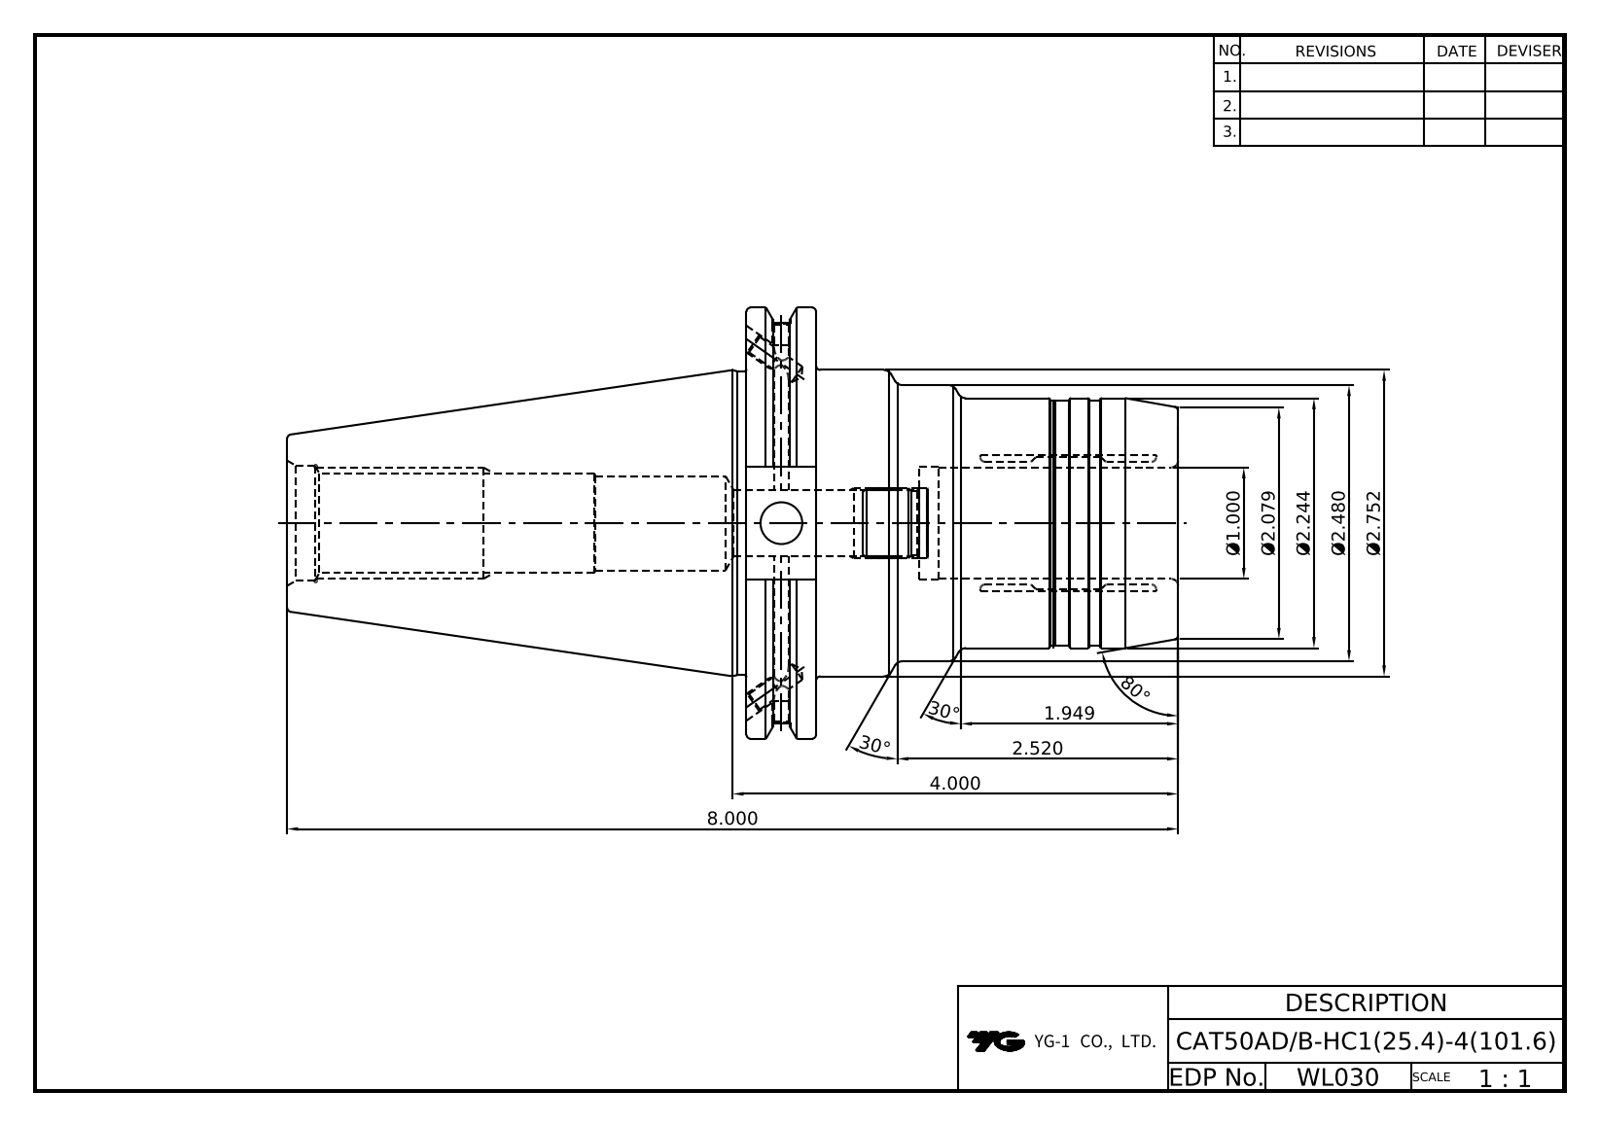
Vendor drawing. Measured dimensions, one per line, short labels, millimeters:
name: LO-CAT50ADB-HC25.4-101.6
written by: Autodesk Inventor 2022 (AUTOMOTIVE_DESIGN)
unit: mm
bodies: 1 solid, 110 faces (37 planar, 33 cylindrical, 40 other)
size: 203.2 × 98.42 × 94.69
volume: 527 991 mm³; area: 64 982 mm²
holes: 2× ⌀3.24, 2× ⌀4.13, 2× ⌀4.2, 2× ⌀5, 1× ⌀9.53, 1× ⌀14.92, 1× ⌀20.5, 1× ⌀21.97, 1× ⌀25.4, 1× ⌀25.8, 1× ⌀26.2
bosses: 1× ⌀98.42, 1× ⌀91.29, 1× ⌀69.9, 1× ⌀69.25, 1× ⌀63, 1× ⌀57, 1× ⌀56
face distances: 15.88, 98.43, 82.55, 104.77, 120.65, 203.2, 144.2, 39.43, 23.55, 59
